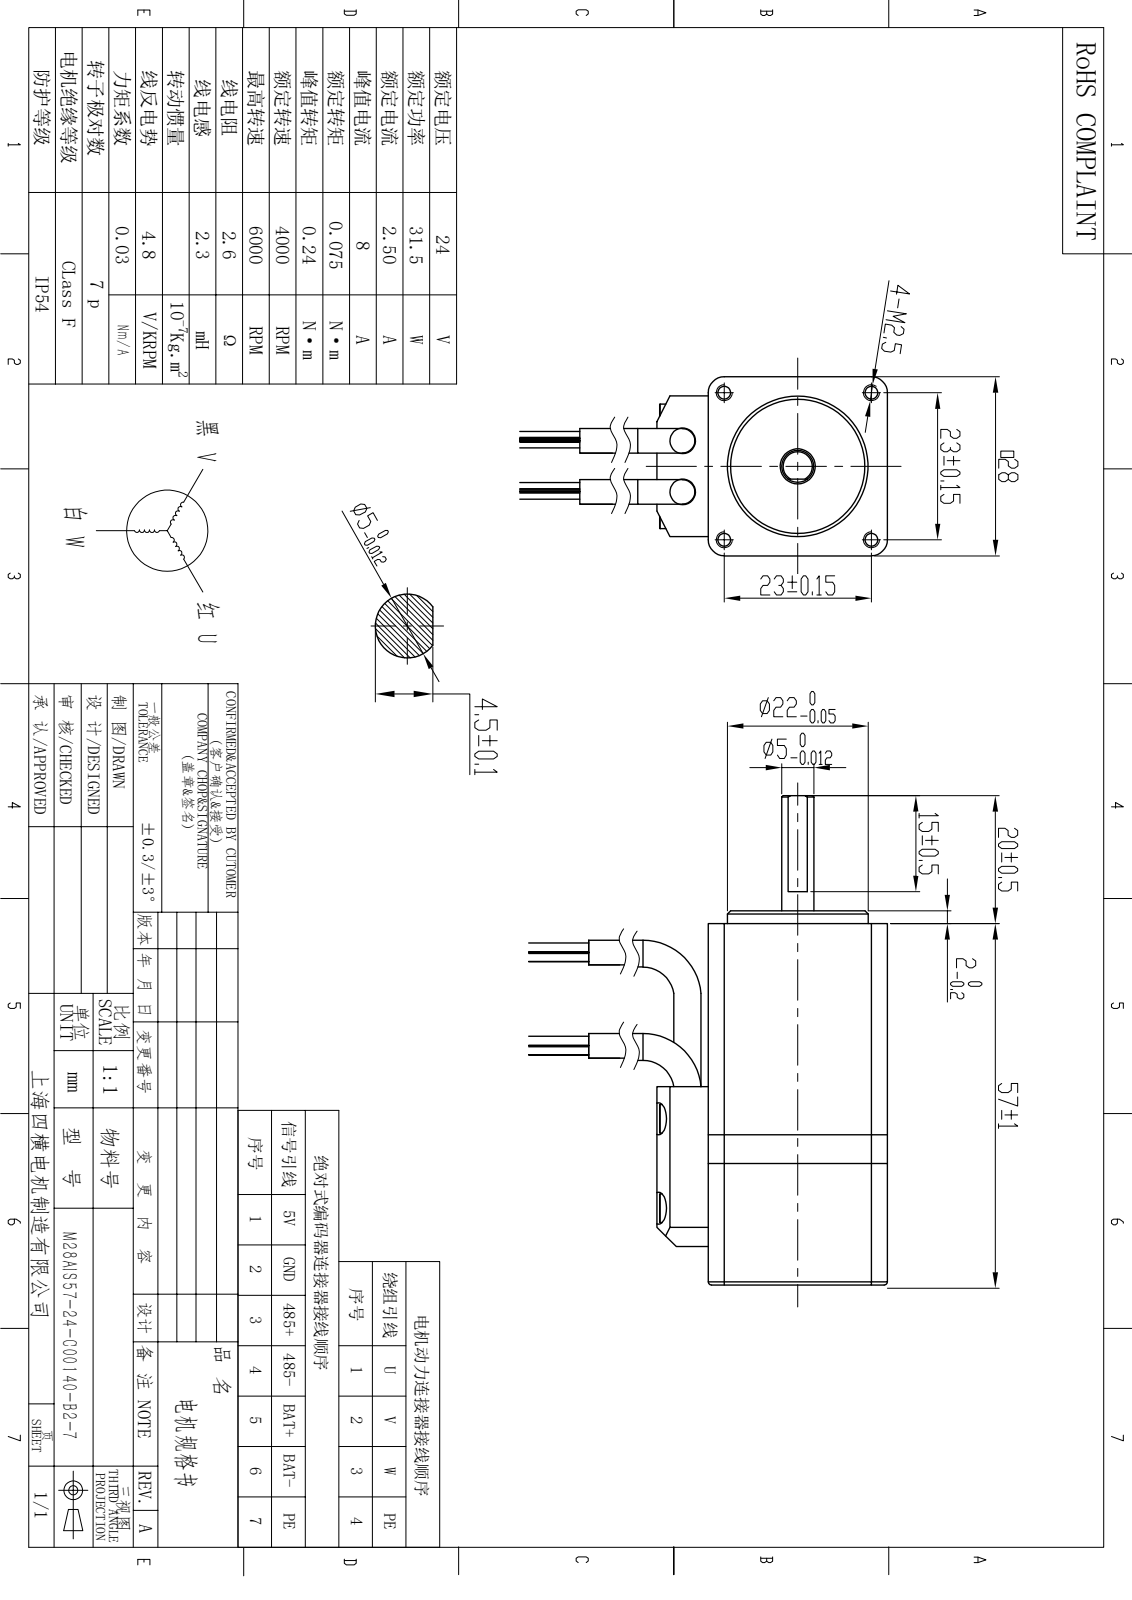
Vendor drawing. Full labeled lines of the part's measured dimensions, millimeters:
Part name (STEP PRODUCT): M28AIS57-24-C00140-B2-7
STEP written by: SolidWorks 2020 (CONFIG_CONTROL_DESIGN)
Units: millimetres
Bodies: 11 solids, 274 faces (134 planar, 89 cylindrical, 51 other)
Overall size (bounding box): 76.5 × 36 × 28
Volume: 27 001 mm³ · Surface area: 21 446 mm²
Round holes (diameter × count): ⌀2.05 ×12, ⌀2.9 ×8, ⌀5 ×8, ⌀1.6 ×2, ⌀4 ×2, ⌀5.5 ×1, ⌀9 ×1, ⌀11 ×1, ⌀12 ×1, ⌀16 ×1, ⌀22 ×1, ⌀23 ×1
Round bosses / shafts (diameter × count): ⌀4.5 ×6, ⌀2.5 ×6, ⌀20 ×1, ⌀13 ×1, ⌀11.6 ×1, ⌀7 ×1, ⌀5 ×1
Partial cylindrical surfaces — rounded edges, fillets, slot ends (radius × count): R0.5 ×4, R2.5 ×4, R1.5 ×2
Main face-to-face distances: 28, 4.5, 19, 33, 4, 2, 5, 3, 2.5, 15
Hole centre spacings: 22.13, 15, 1.26, 16.26, 17.77, 18.84, 21.22, 23
